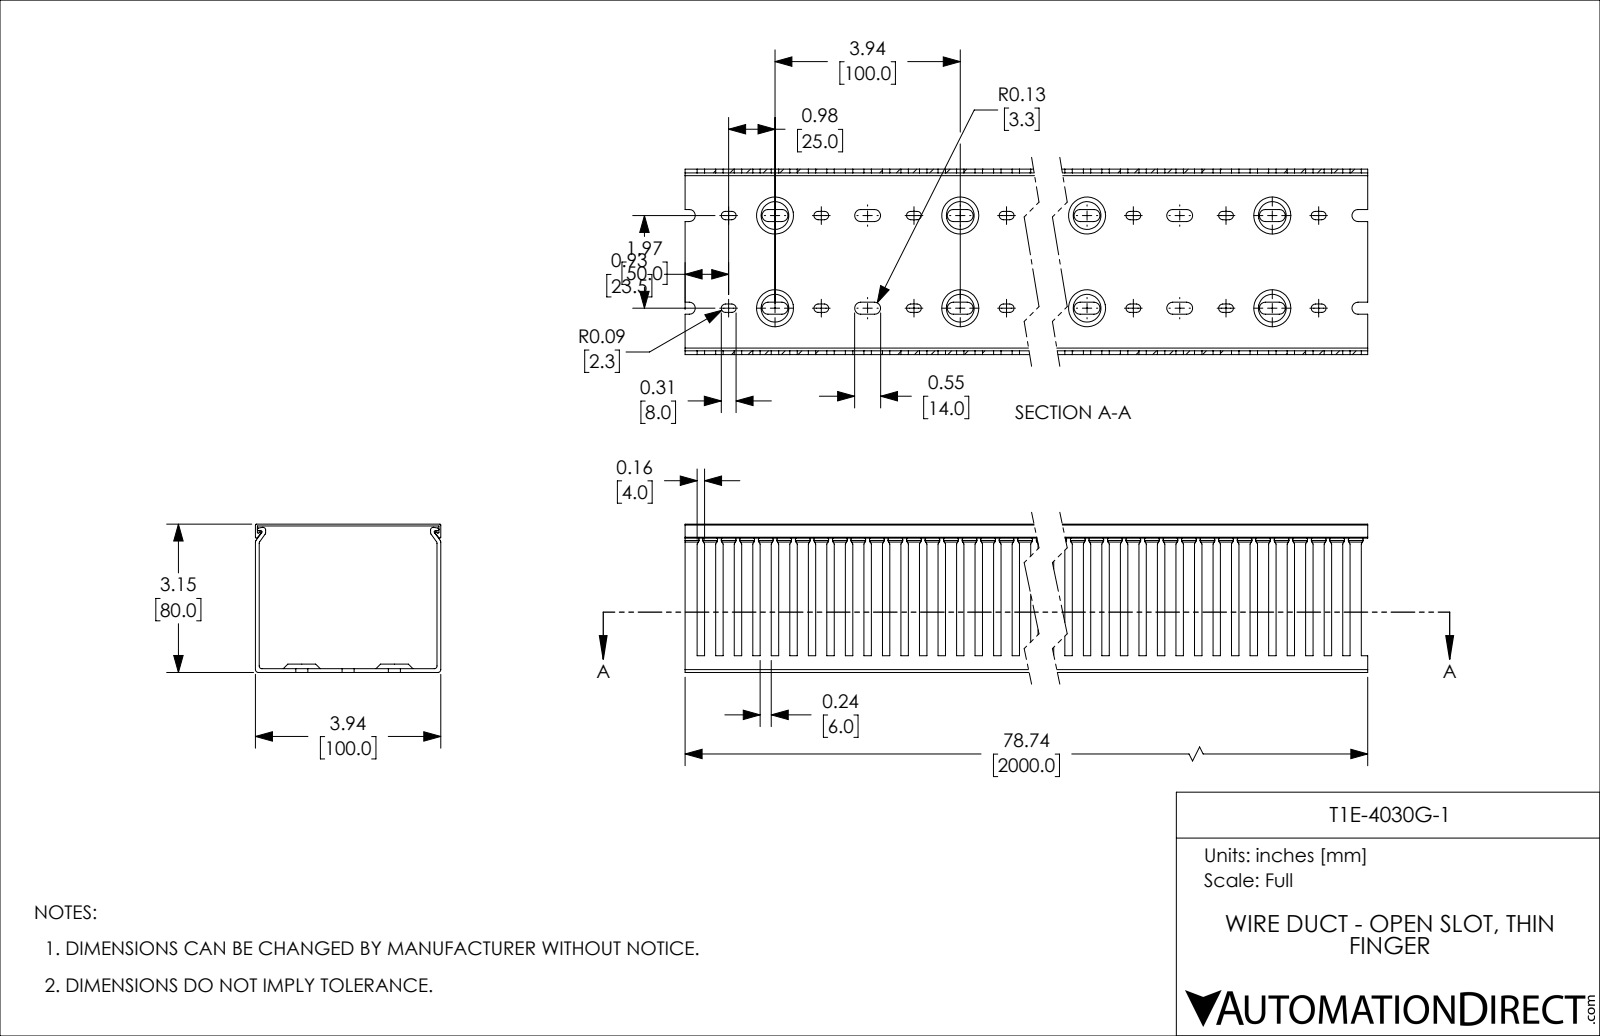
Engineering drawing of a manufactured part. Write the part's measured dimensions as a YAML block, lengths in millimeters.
part_name: "T1E-4030G-1"
step_written_by: "SolidWorks 2021 (CONFIG_CONTROL_DESIGN)"
units: millimeters
bodies: {solids: 2, faces: 1573, planar: 762, cylindrical: 731, other: 80}
overall_size: [2000, 100, 80]
volume: 1254000
surface_area: 1494000
partial_cylinders:
  - {radius: 3.25, count: 200}
  - {radius: 2.25, count: 160}
  - {radius: 1.5, count: 12}
  - {radius: 0.5, count: 8}
  - {radius: 0.75, count: 6}
face_to_face_distances: [2, 98, 1, 80, 79, 77, 78, 100, 96, 99]
